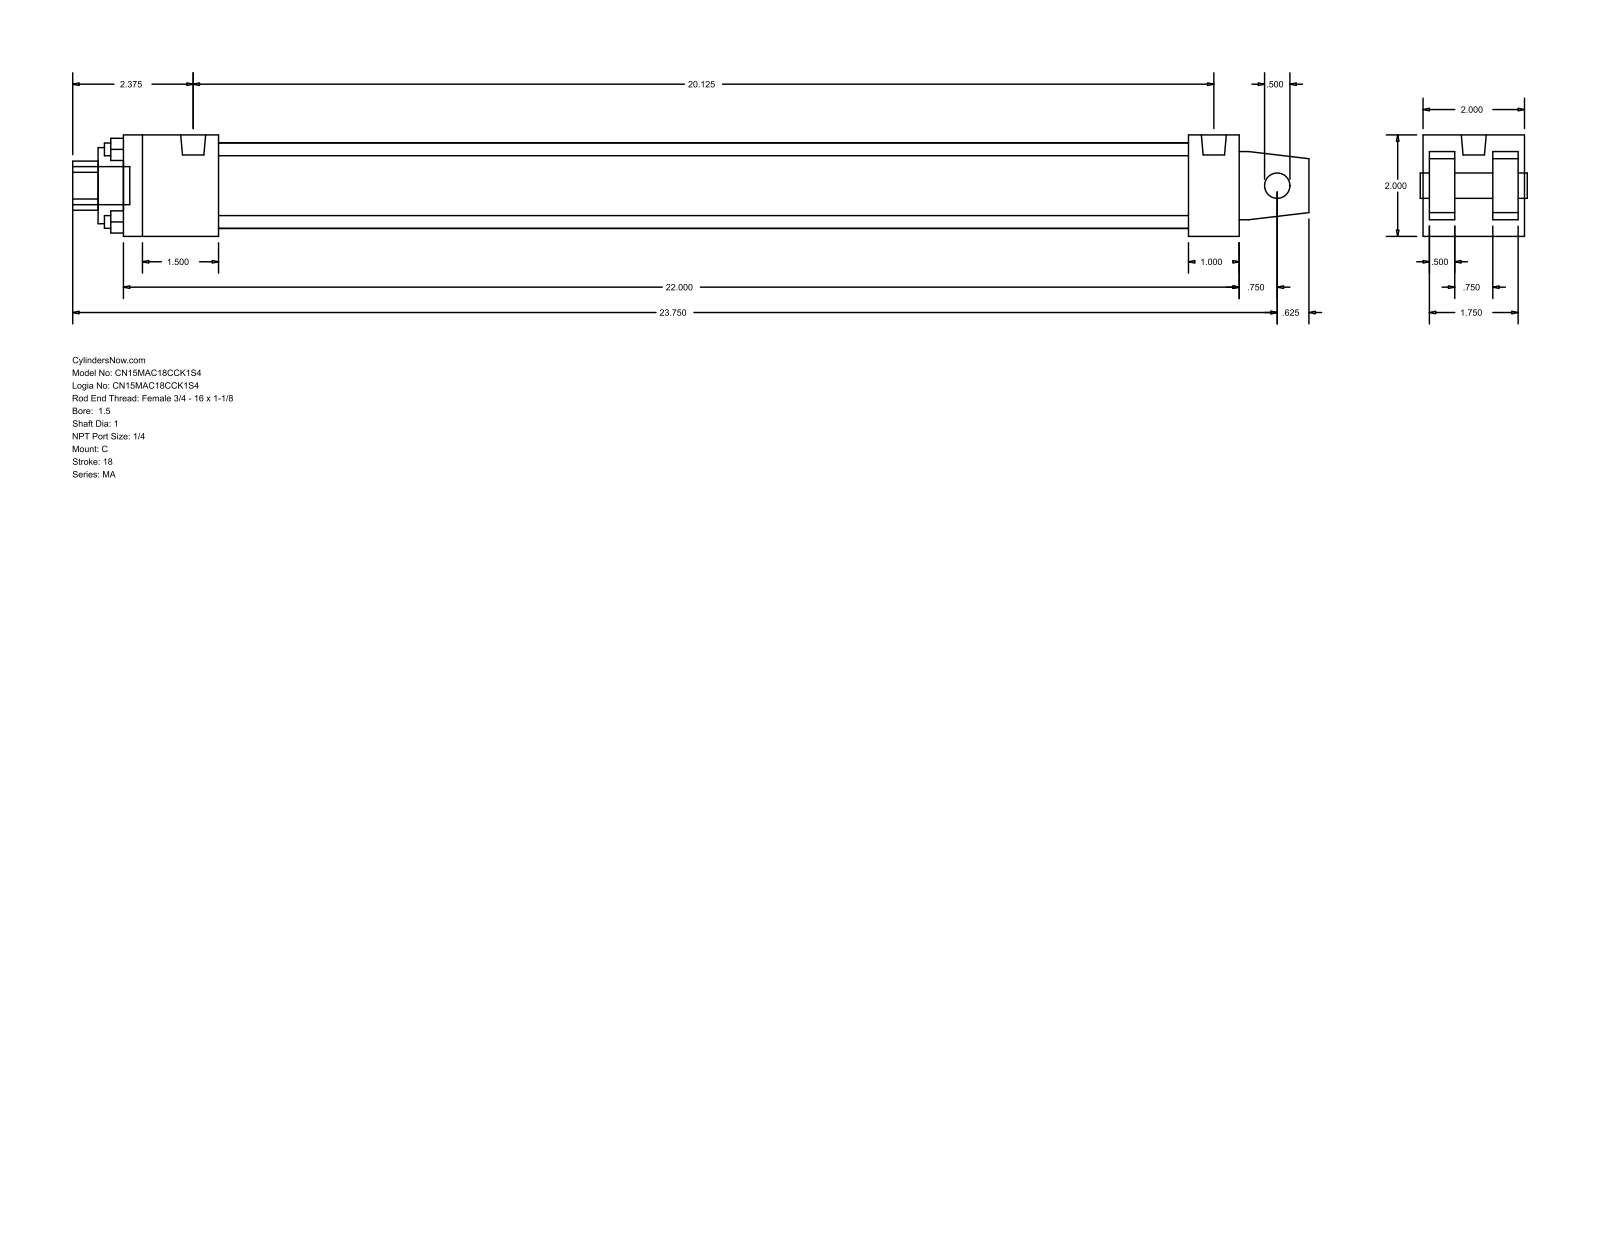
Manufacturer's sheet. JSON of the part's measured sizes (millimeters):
{"part_name": "MA_C__0150_1", "step_written_by": "GSSL Pune (CONFIG_CONTROL_DESIGN)", "units": "millimeters", "bodies": {"solids": 0, "faces": 103, "planar": 76, "cylindrical": 27, "other": 0}, "overall_size": [619.12, 50.8, 50.8], "round_holes": [[6.35, 4], [12.7, 1], [25.4, 1], [38.1, 1], [42.93, 1]], "round_bosses_or_shafts": [[7.94, 4], [12.49, 2], [19.05, 1]], "partial_cylinders_radius": [[12.29, 1]], "face_to_face_distances": [50.8, 47.63, 12.7, 3.17, 15.87, 34.93, 31.76, 44.46, 558.8, 25.4], "hole_center_spacings": [25.68, 36.32, 51.36]}
